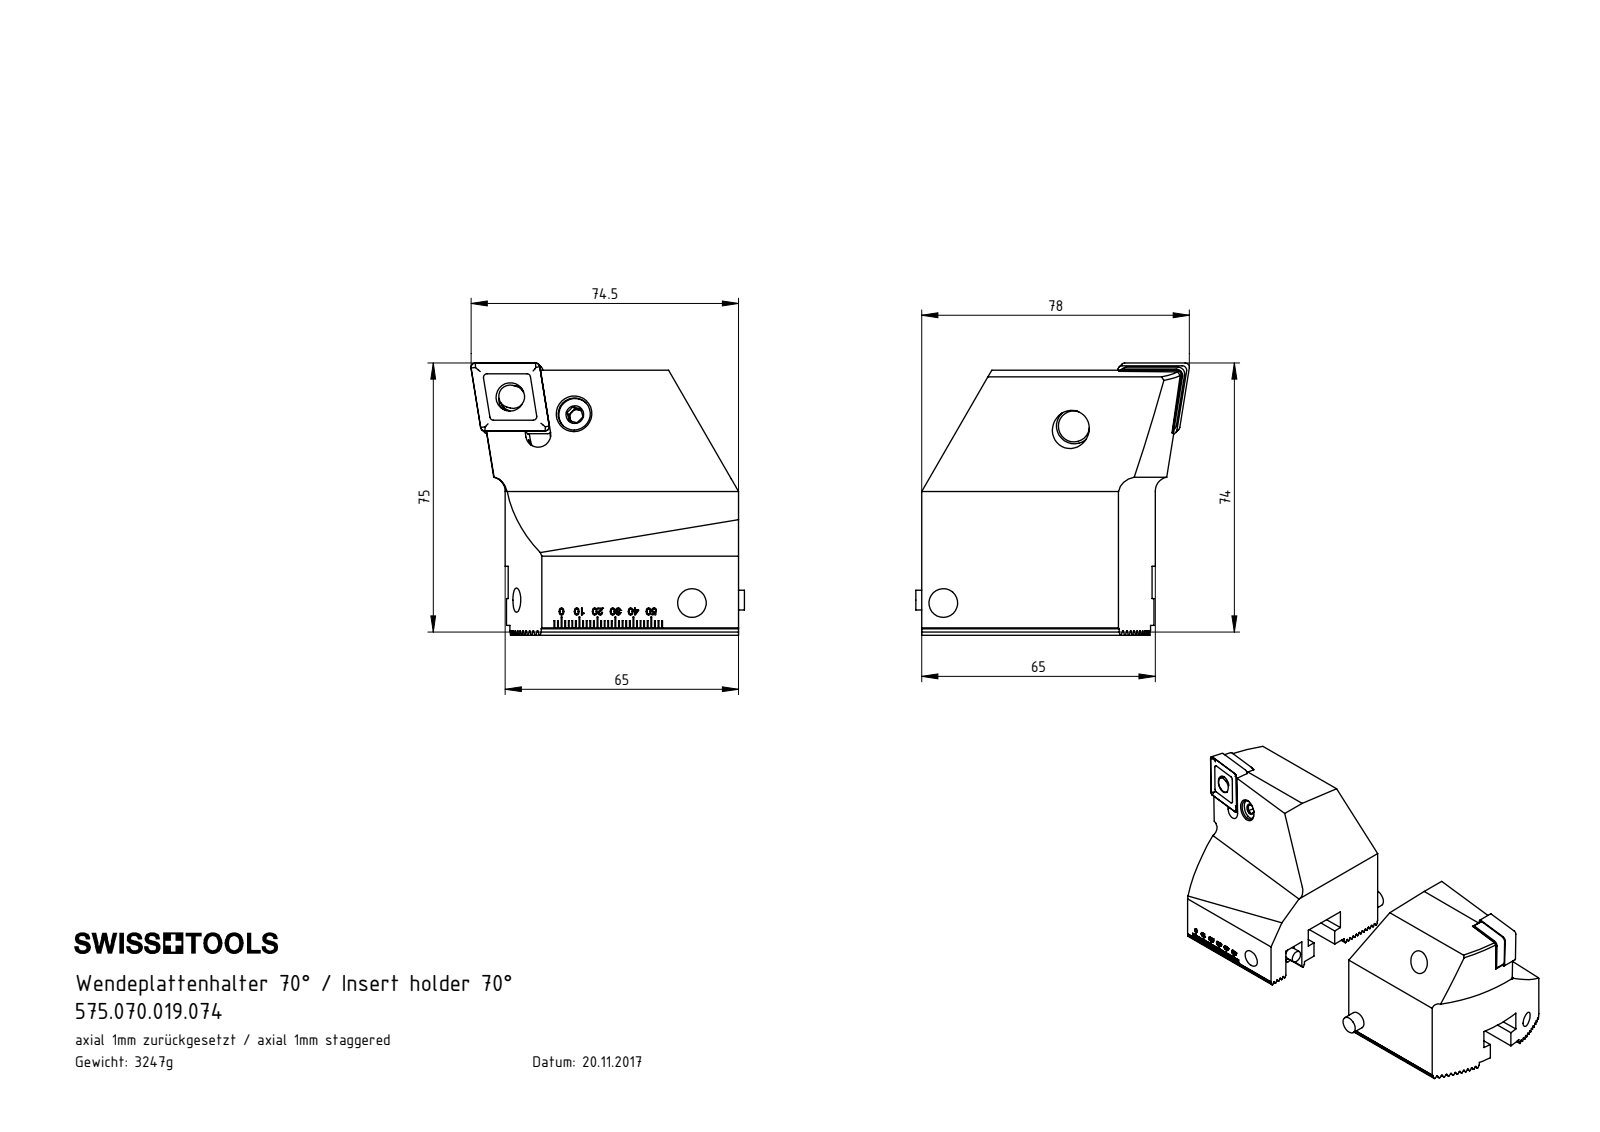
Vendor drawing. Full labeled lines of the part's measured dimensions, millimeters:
Part name (STEP PRODUCT): WCF-ER1.101.000; ISO 4028 - M8 x 35; WCF; VK1-WCF.101.075_A (+6 more)
STEP written by: SolidWorks 2017 (CONFIG_CONTROL_DESIGN)
Units: millimetres
Bodies: 16 solids, 1300 faces (784 planar, 170 cylindrical, 346 other)
Overall size (bounding box): 200.04 × 83.92 × 75.79
Volume: 410 334 mm³ · Surface area: 73 404 mm²
Round holes (diameter × count): ⌀8 ×4, ⌀6.8 ×2, ⌀7.94 ×2, ⌀9 ×2, ⌀9.6 ×2, ⌀10.2 ×2
Round bosses / shafts (diameter × count): ⌀10 ×2, ⌀9.9 ×2, ⌀8.6 ×2, ⌀8 ×2, ⌀5.5 ×2, ⌀4.45 ×2
Partial cylindrical surfaces — rounded edges, fillets, slot ends (radius × count): R0.14 ×22, R1.2 ×8, R1.8 ×8, R4.15 ×8, R4.7 ×3, R3.1 ×2, R3.5 ×2, R3.65 ×2
Main face-to-face distances: 1.73, 6.93, 8.66, 70, 3.46, 5.2, 41.57, 43.3, 24.5, 45.5
Hole centre spacings: 7, 18.52, 70, 0.31, 0.32, 18.8, 18.81, 40
